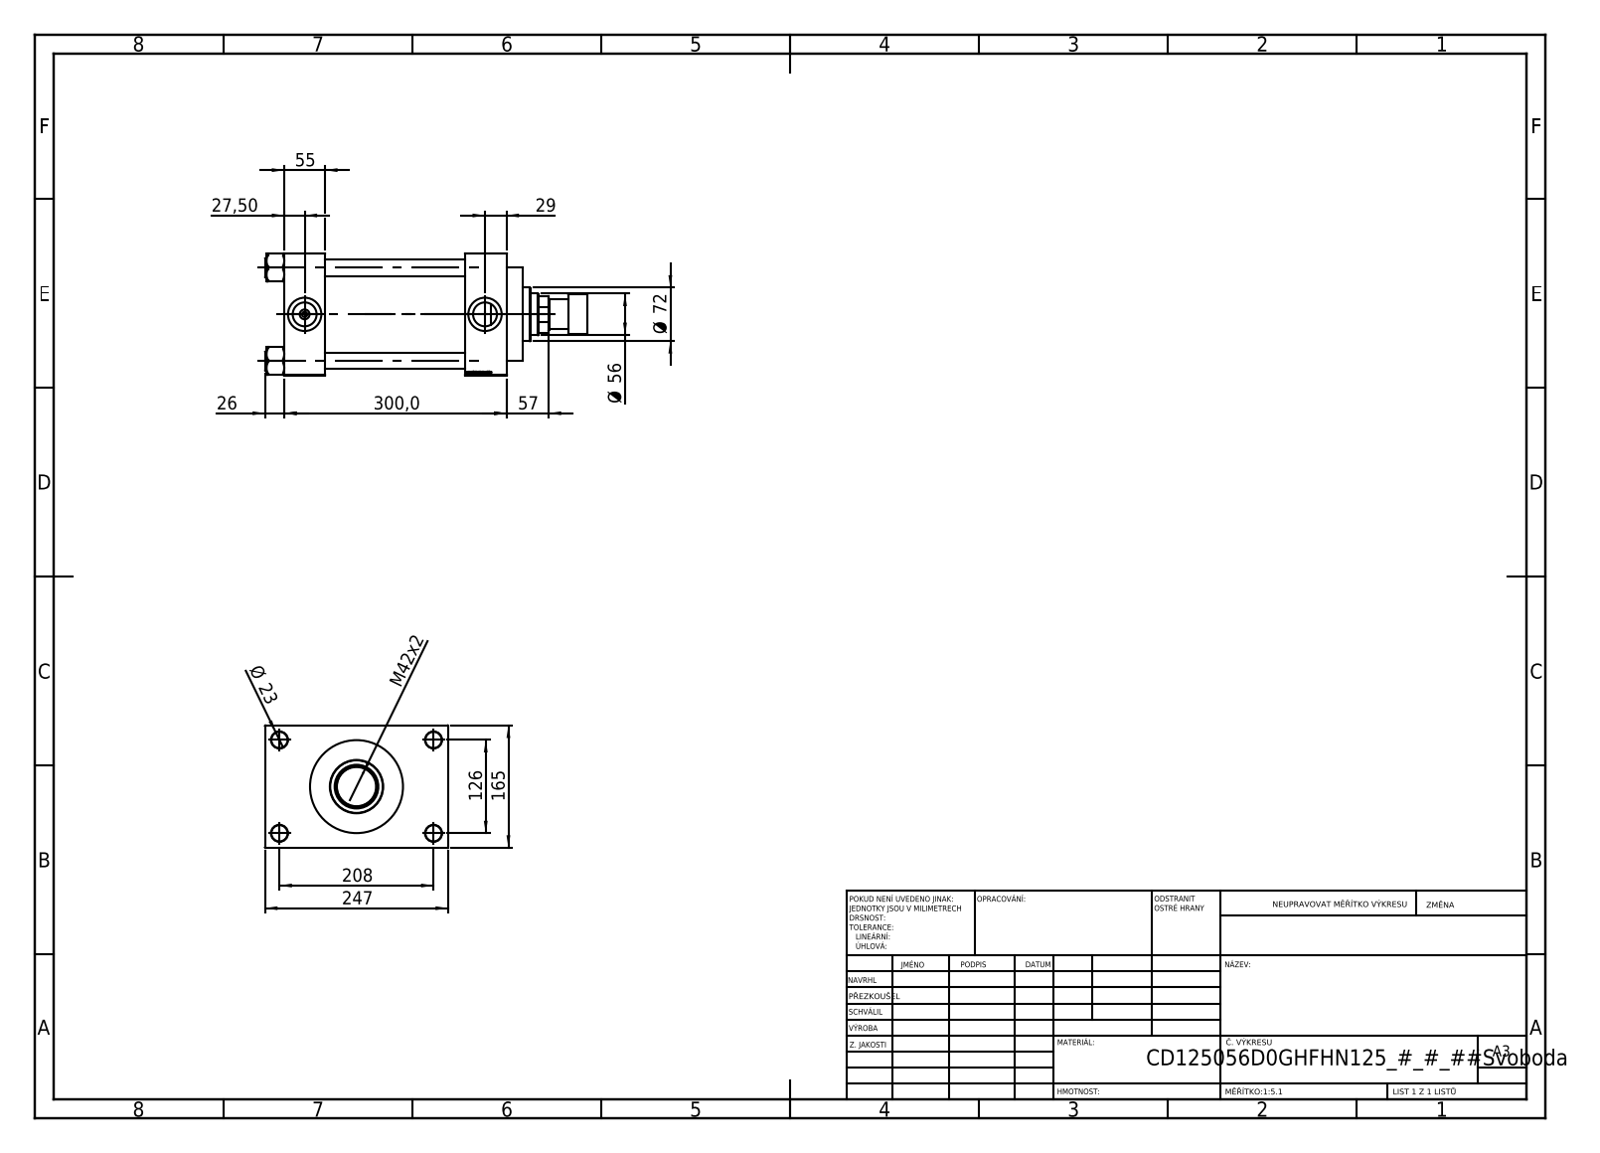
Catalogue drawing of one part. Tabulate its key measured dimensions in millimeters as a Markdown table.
| quantity | value |
| --- | --- |
| part name | V215CD_D_TYCINKA; V215CD_D_Body; V215CD_NUT_M5_D; V215CD_VCP_D (+2 more) |
| STEP written by | SolidWorks 2019 (CONFIG_CONTROL_DESIGN) |
| units | millimeters |
| bodies | 12 solids, 1162 faces (548 planar, 90 cylindrical, 524 other) |
| overall size | 435 × 247 × 165 |
| volume | 5 562 000 mm³ |
| surface area | 678 545 mm² |
| round holes (diameter × count) | 22 × 8, 7 × 2, 32.24 × 2, 45 × 2, 40.5 × 1, 56 × 1, 59 × 1, 96 × 1, 125 × 1, 125.5 × 1 |
| round bosses / shafts (diameter × count) | 25 × 4, 131 × 1, 72 × 1, 54 × 1, 40 × 1 |
| main face-to-face distances | 165, 189, 244, 55, 245, 56, 300, 41, 206, 278.74 |
| hole center spacings | 41.05, 89.02, 121.59, 125.9, 132.47, 166.95, 209.13, 126 |
